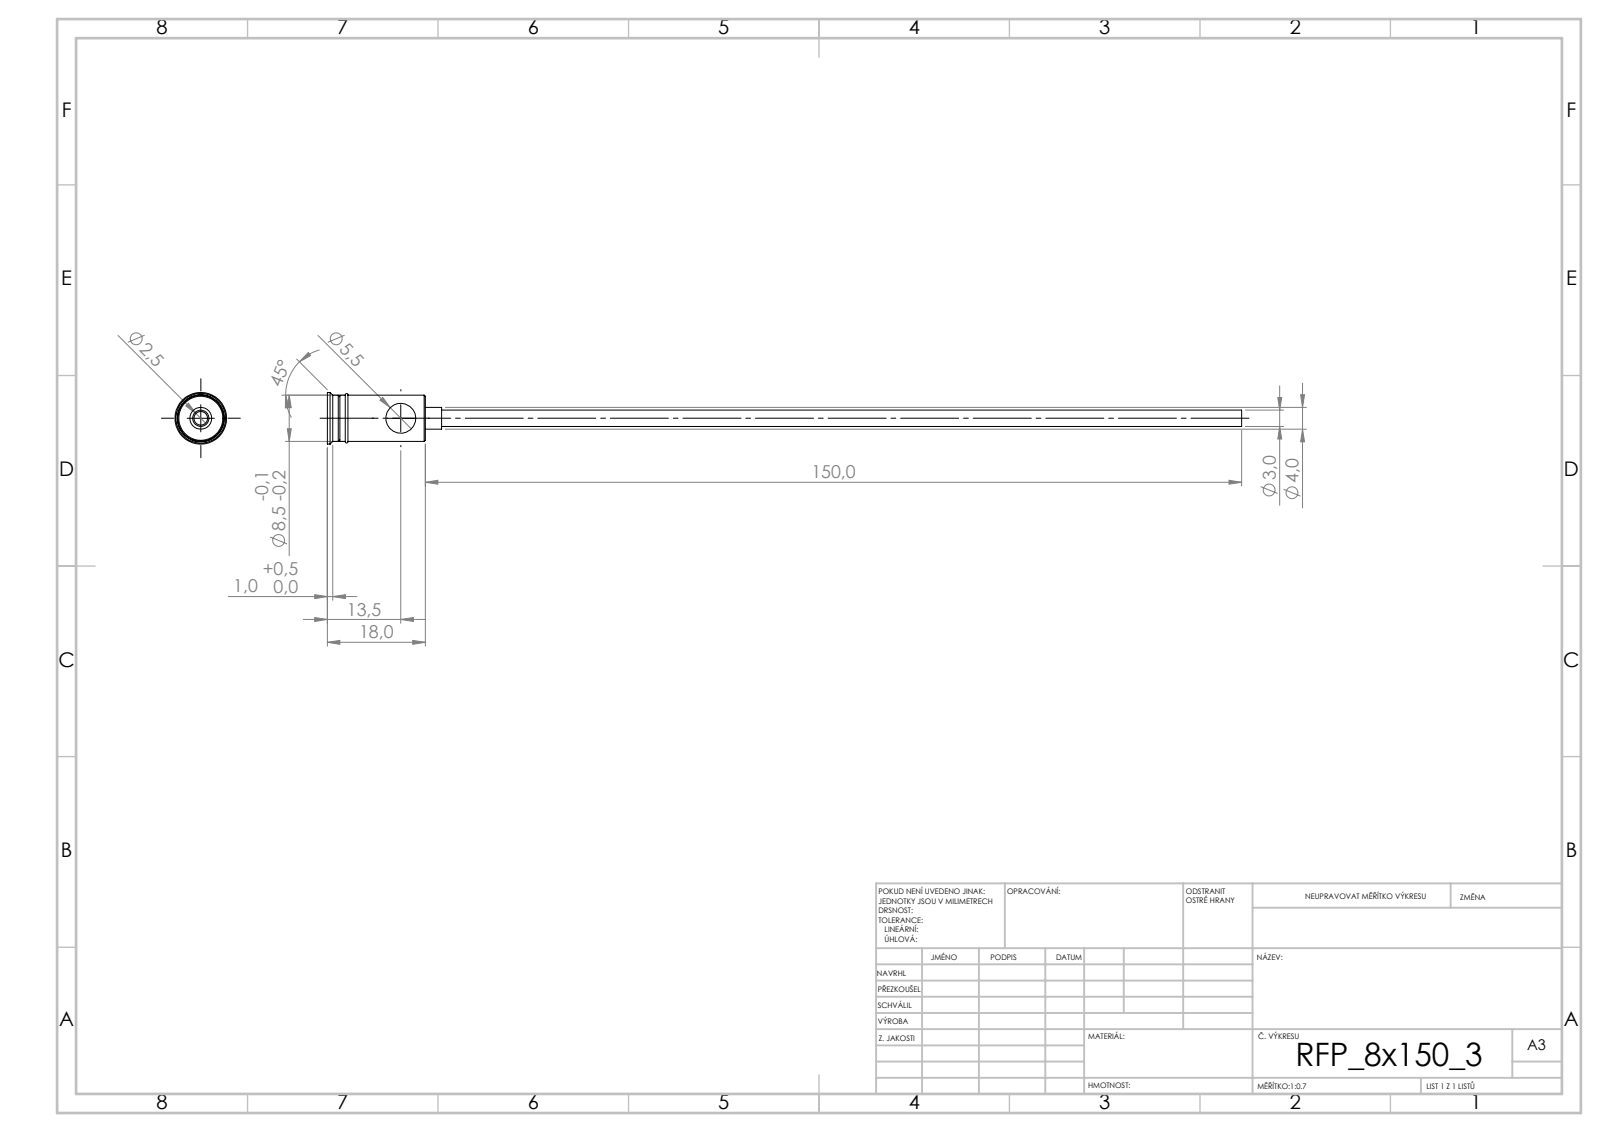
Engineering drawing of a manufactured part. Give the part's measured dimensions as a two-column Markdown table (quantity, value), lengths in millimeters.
| quantity | value |
| --- | --- |
| STEP written by | SolidWorks 2019 (CONFIG_CONTROL_DESIGN) |
| units | millimeters |
| bodies | 1 solid, 44 faces (20 planar, 16 cylindrical, 8 other) |
| overall size | 168 × 9.5 × 9.5 |
| volume | 1 148 mm³ |
| surface area | 3 346 mm² |
| round holes (diameter × count) | 2.5 × 1, 5.5 × 1 |
| round bosses / shafts (diameter × count) | 9.5 × 1, 8.5 × 1, 4 × 1, 3 × 1 |
| main face-to-face distances | 18, 16, 2, 3.9, 15.7, 2.3, 3, 18.7, 19, 21 |
